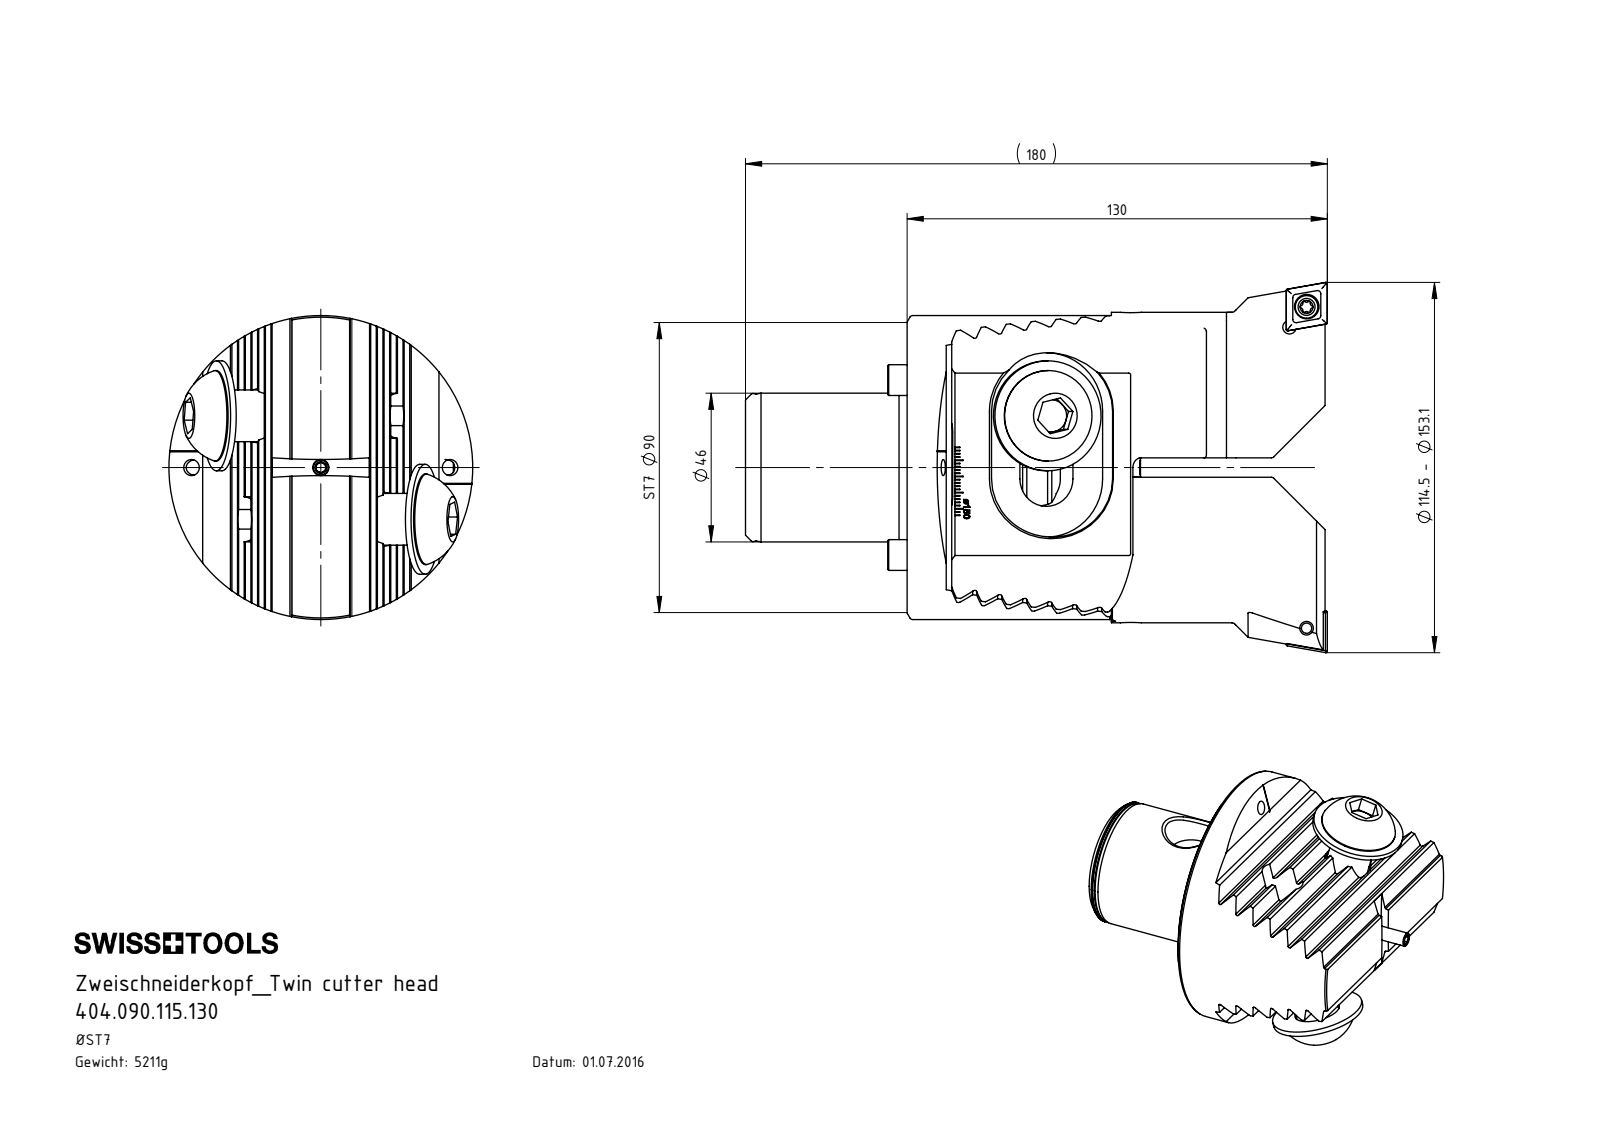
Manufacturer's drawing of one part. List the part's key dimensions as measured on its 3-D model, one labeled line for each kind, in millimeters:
Part name (STEP PRODUCT): Z42-ER2.001.019_A; Z94-ER1.001.035; Z94-ER1.003.035_A_gespannt; Z94-ER1.002.035_A (+3 more)
STEP written by: SolidWorks 2015 (CONFIG_CONTROL_DESIGN)
Units: millimetres
Bodies: 8 solids, 358 faces (139 planar, 107 cylindrical, 112 other)
Overall size (bounding box): 122.2 × 94 × 94
Volume: 322 189 mm³ · Surface area: 60 411 mm²
Round holes (diameter × count): ⌀5 ×3, ⌀6 ×2, ⌀14 ×2, ⌀17 ×2, ⌀17.5 ×2, ⌀3.3 ×1, ⌀15 ×1, ⌀22 ×1, ⌀25 ×1
Round bosses / shafts (diameter × count): ⌀34 ×2, ⌀28 ×2, ⌀16 ×2, ⌀94 ×1, ⌀46 ×1, ⌀45.8 ×1, ⌀45.3 ×1, ⌀5 ×1
Partial cylindrical surfaces — rounded edges, fillets, slot ends (radius × count): R0.58 ×14, R0.5 ×4, R6.97 ×2, R23.05 ×2, R220 ×2
Main face-to-face distances: 6.93, 13.86, 27.71, 20.78, 13.85, 34.64, 20.79, 6.92, 63.2, 1.8
Hole centre spacings: 28, 23.4, 56
